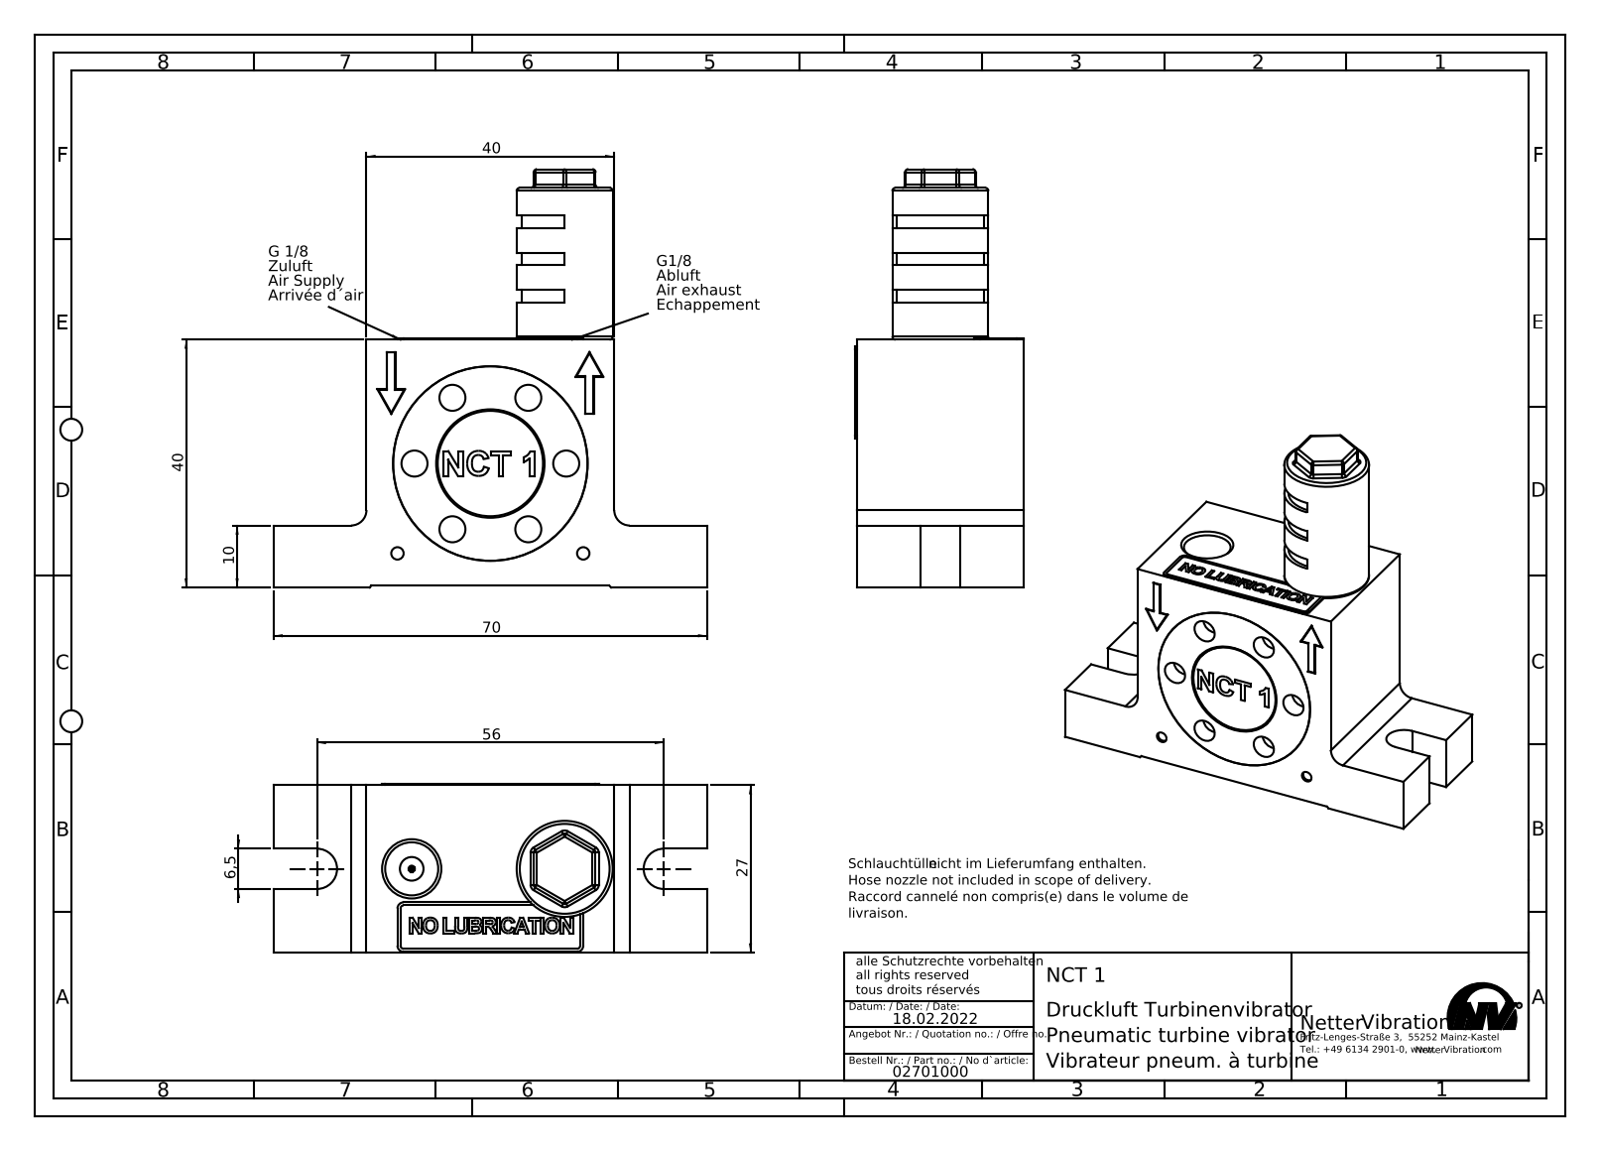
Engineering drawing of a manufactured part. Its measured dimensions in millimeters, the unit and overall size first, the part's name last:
Units: millimetres
Overall size (bounding box): 70 × 67.5 × 27.45
Round holes (diameter × count): ⌀4.2 ×6, ⌀2 ×2, ⌀8.57 ×2, ⌀14 ×1, ⌀17.5 ×1, ⌀19 ×1, ⌀29.5 ×1
Round bosses / shafts (diameter × count): ⌀32 ×1, ⌀29.47 ×1, ⌀27.27 ×1, ⌀17 ×1, ⌀15.5 ×1, ⌀9.73 ×1
Partial cylindrical surfaces — rounded edges, fillets, slot ends (radius × count): R0.5 ×22, R1 ×4, R2.5 ×2, R3.25 ×2, R7 ×1
Main face-to-face distances: 40, 27, 39.7, 4, 23, 27.15, 10, 30, 9.7, 23.2
Hole centre spacings: 12.25, 21.21, 24.5, 9.69, 12.24, 14.76, 20.86, 21.22
Volume: 55 001 mm³ · Surface area: 17 710 mm²
Bodies: 6 solids, 388 faces (242 planar, 79 cylindrical, 67 other)
Part name (STEP PRODUCT): NCT 1 Turbinenvibrator #02701000
STEP written by: SolidWorks 2015 (AUTOMOTIVE_DESIGN)
